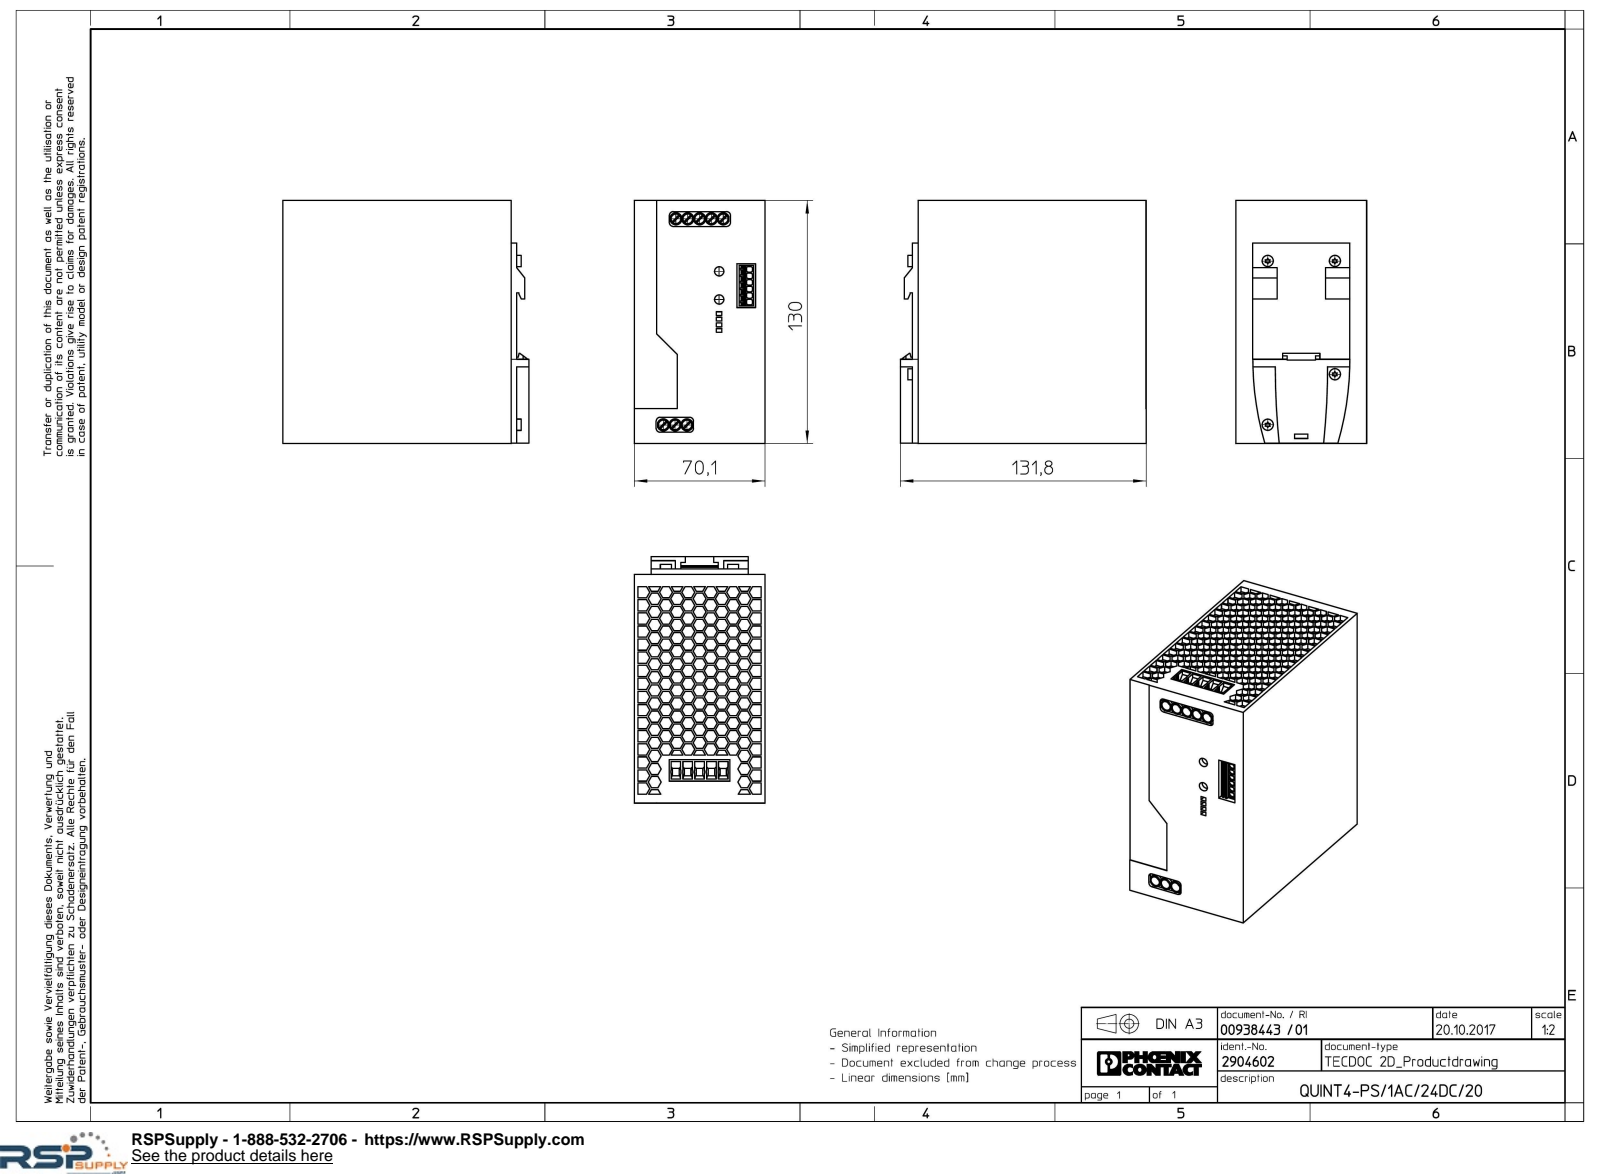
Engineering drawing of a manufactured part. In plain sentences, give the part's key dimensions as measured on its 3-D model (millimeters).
The part is named "QUINT4_PS_1AC_24DC_20_SIDE-MOUNTED-select". Its 3-D file was written by "Creo Elements/Direct Modeling 20.1A 29-Sep-2018 (C) Parametric Technology GmbH (AUTOMOTIVE_DESIGN)". It is 1 solid with 2816 faces: 2720 planar, 76 cylindrical and 20 other. Overall it measures 130 by 122.95 by 79.6 millimeters. Its volume is 1 124 000 cubic millimeters and its surface area 78 758 square millimeters. Round holes: 8 of diameter 5. Round bosses or shafts: 4 of diameter 6, 2 of diameter 5. Partial cylindrical surfaces (rounded edges, fillets, slot ends): 12 of radius 0.97, 8 of radius 2.5, 8 of radius 3.25, 6 of radius 0.57, 6 of radius 0.6. The main face-to-face distances are 70, 122.25, 0.8, 129.2, 128.4, 3, 73, 130, 122.15, 6.5. The hole center spacings are 6.35, 12.7, 19.05, 25.4.
